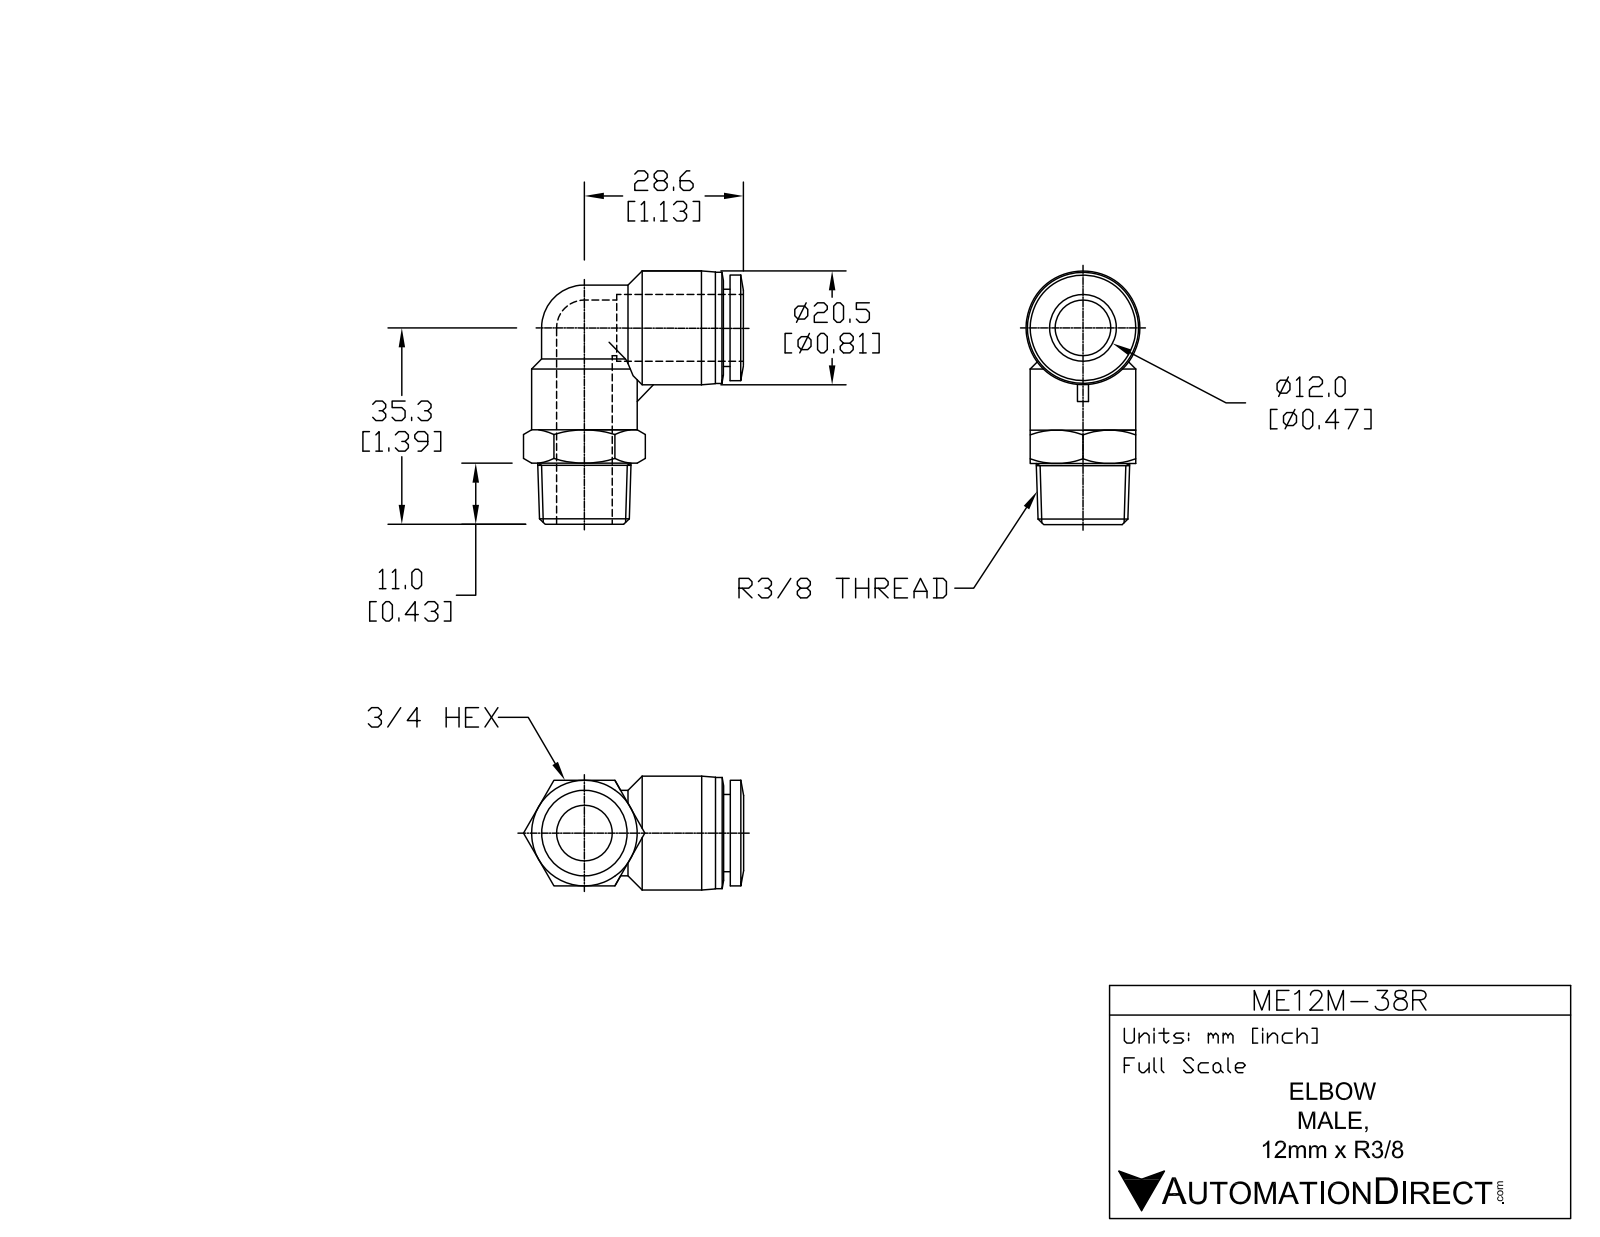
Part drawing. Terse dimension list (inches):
name: ME12M-38R
written by: SolidWorks 2015 (AUTOMOTIVE_DESIGN)
unit: in
bodies: 1 solid, 68 faces (16 planar, 19 cylindrical, 33 other)
size: 1.797 × 1.56 × 0.807
volume: 0.636 in³; area: 10.01 in²
holes: 2× ⌀0.394, 1× ⌀0.484
bosses: 2× ⌀0.748, 1× ⌀0.807, 1× ⌀0.787, 1× ⌀0.606, 1× ⌀0.547
rounds: 1× R0.303
face distances: 0.748, 0.047, 0.433, 0.76, 0.807, 0.902, 0.142, 0.094, 0.335, 0.413
